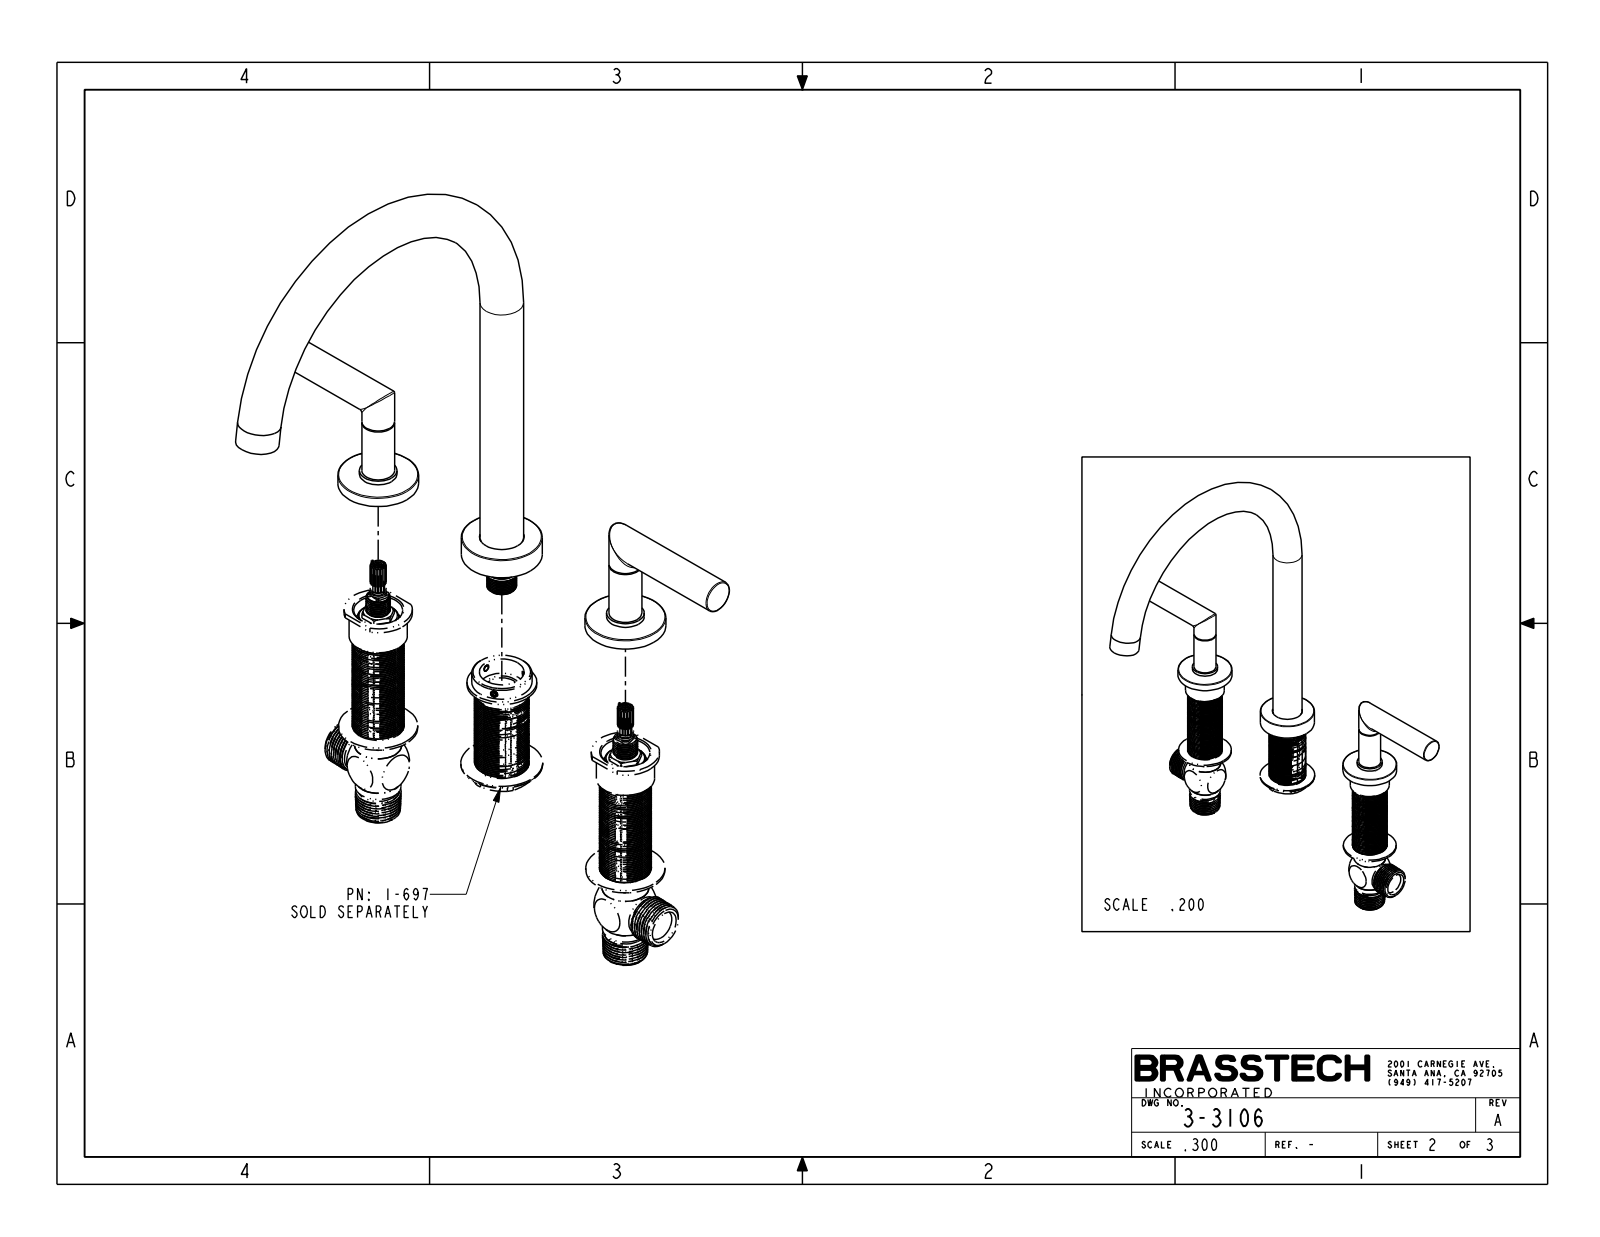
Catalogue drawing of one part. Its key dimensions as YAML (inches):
part_name: "3-3106"
step_written_by: "CREO PARAMETRIC BY PTC INC, 2018400 (CONFIG_CONTROL_DESIGN)"
units: inches
bodies: {solids: 3, faces: 77, planar: 19, cylindrical: 38, other: 20}
overall_size: [14, 11.513, 9.335]
volume: 22.05
surface_area: 106.8
round_holes:
  - {diameter: 0.76, count: 2}
round_bosses_or_shafts:
  - {diameter: 1.85, count: 3}
  - {diameter: 0.75, count: 3}
  - {diameter: 1, count: 2}
  - {diameter: 0.86, count: 2}
  - {diameter: 0.506, count: 2}
face_to_face_distances: [0.25, 0.5, 1.701, 1.732, 1.451, 1.482, 1.201, 1.232, 0.031, 14]
hole_center_spacings: [8]
